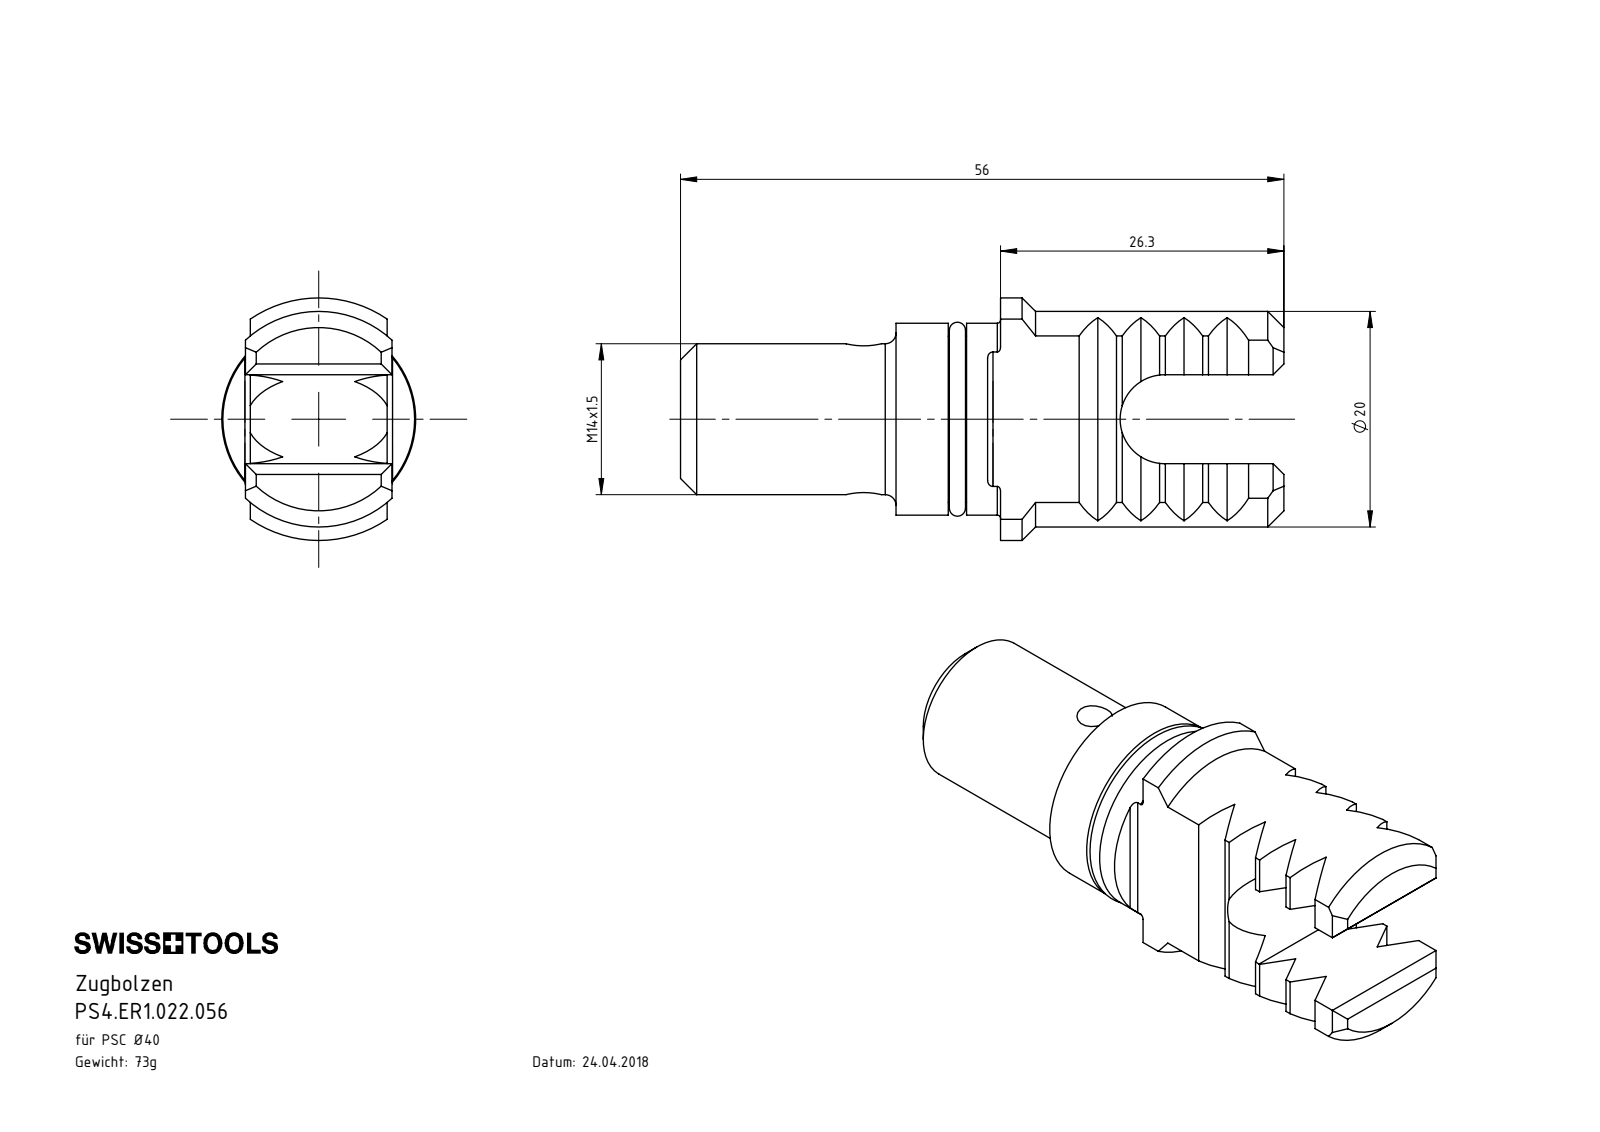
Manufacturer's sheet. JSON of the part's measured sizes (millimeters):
{"part_name": "PS4-ER1.022.056_A; DIN 3771 - 15x1.5; PS4-ER1.022.056", "step_written_by": "SolidWorks 2017 (AUTOMOTIVE_DESIGN)", "units": "millimeters", "bodies": {"solids": 2, "faces": 106, "planar": 62, "cylindrical": 23, "other": 21}, "overall_size": [56, 22.5, 18], "volume_mm3": 9326, "surface_area_mm2": 4477, "round_holes": [[3.3, 1], [4.2, 1]], "round_bosses_or_shafts": [[17.8, 1], [15.4, 1], [14, 1]], "partial_cylinders_radius": [[0.5, 2], [4.12, 1], [10, 1], [11.25, 1]], "face_to_face_distances": [3.35, 3.46, 6.81, 12.7, 10.39, 6.93, 6.92, 3.47, 8.24, 4.85]}
